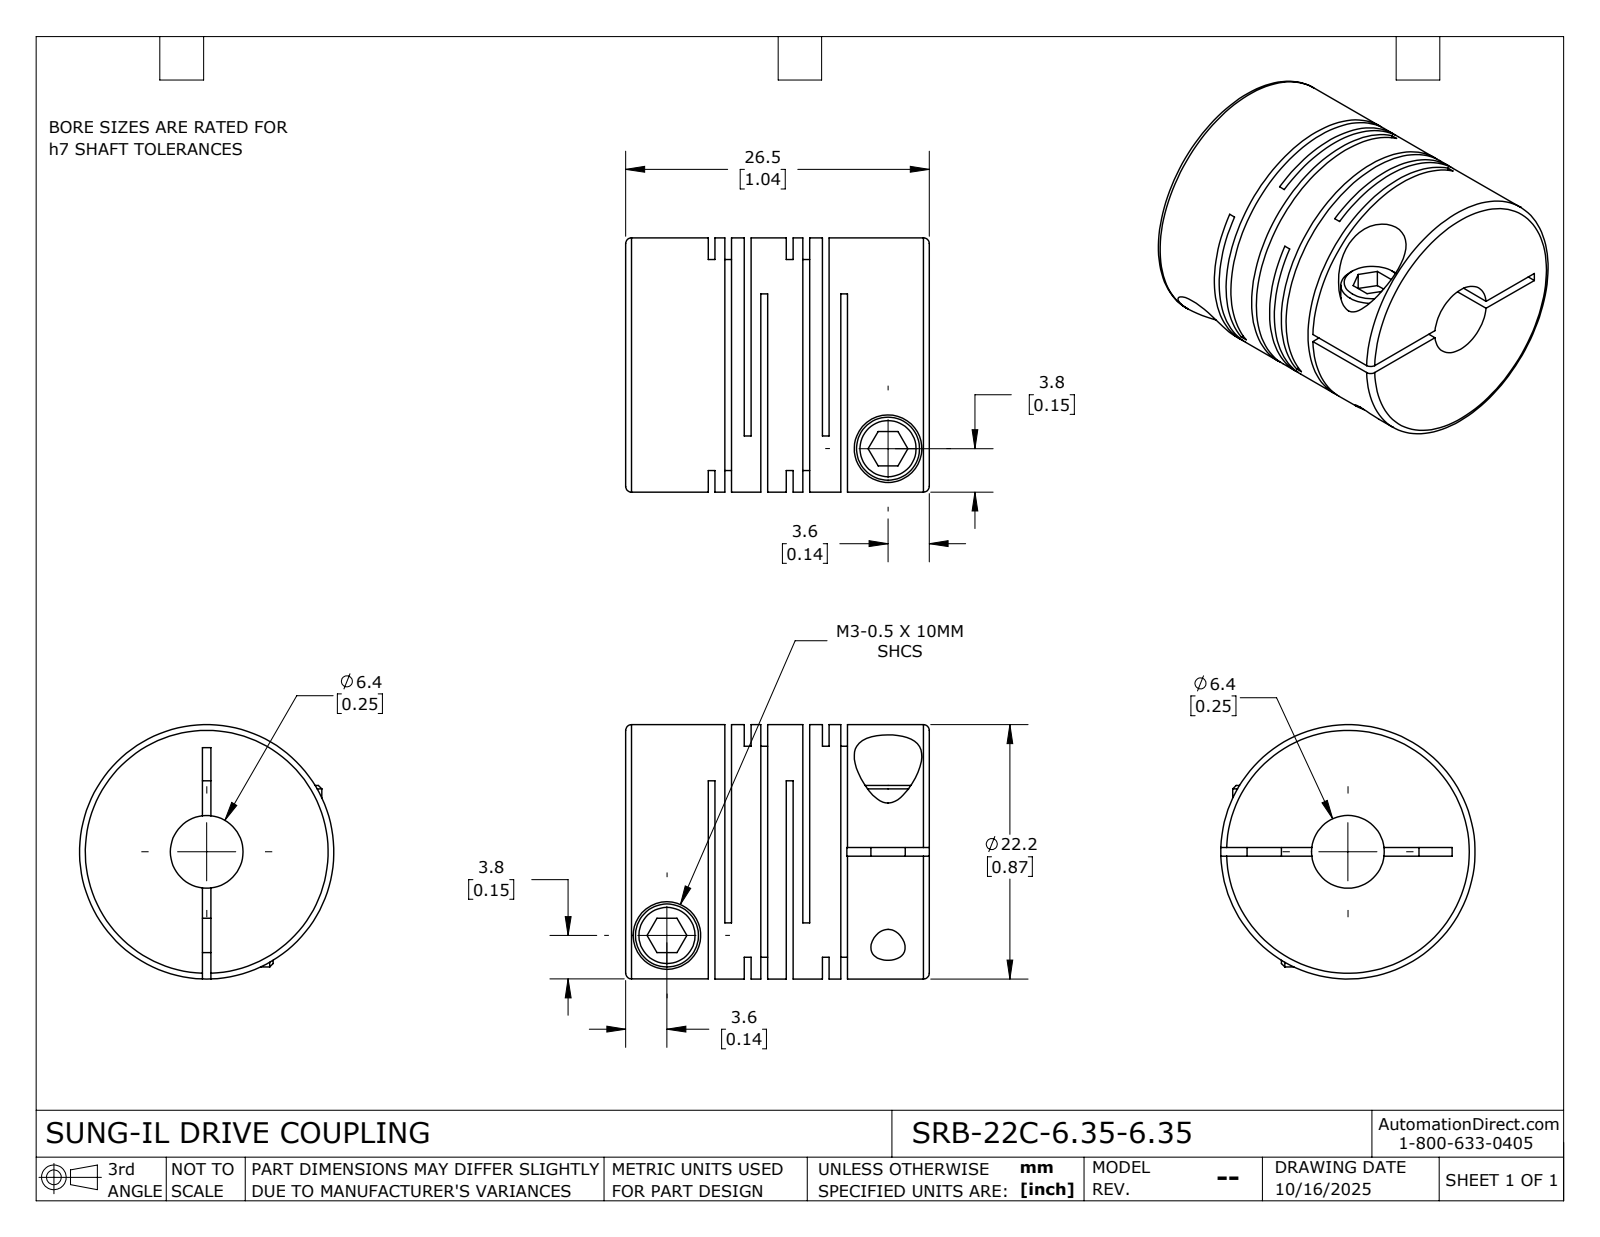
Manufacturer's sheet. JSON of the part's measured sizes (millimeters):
{"part_name": "SRB-22C-6.35-6.35", "step_written_by": "SolidWorks 2024 (CONFIG_CONTROL_DESIGN)", "units": "millimeters", "bodies": {"solids": 1, "faces": 115, "planar": 60, "cylindrical": 42, "other": 13}, "overall_size": [26.5, 22.2, 22.2], "volume_mm3": 7703, "surface_area_mm2": 8105, "round_holes": [[3, 2], [5.9, 2], [6.35, 1]], "round_bosses_or_shafts": [[5.5, 2], [22.2, 1]], "face_to_face_distances": [0.59, 6.82, 1.45, 3.15, 5.37, 1.7, 3.67, 6.23, 0.86, 2.56]}
